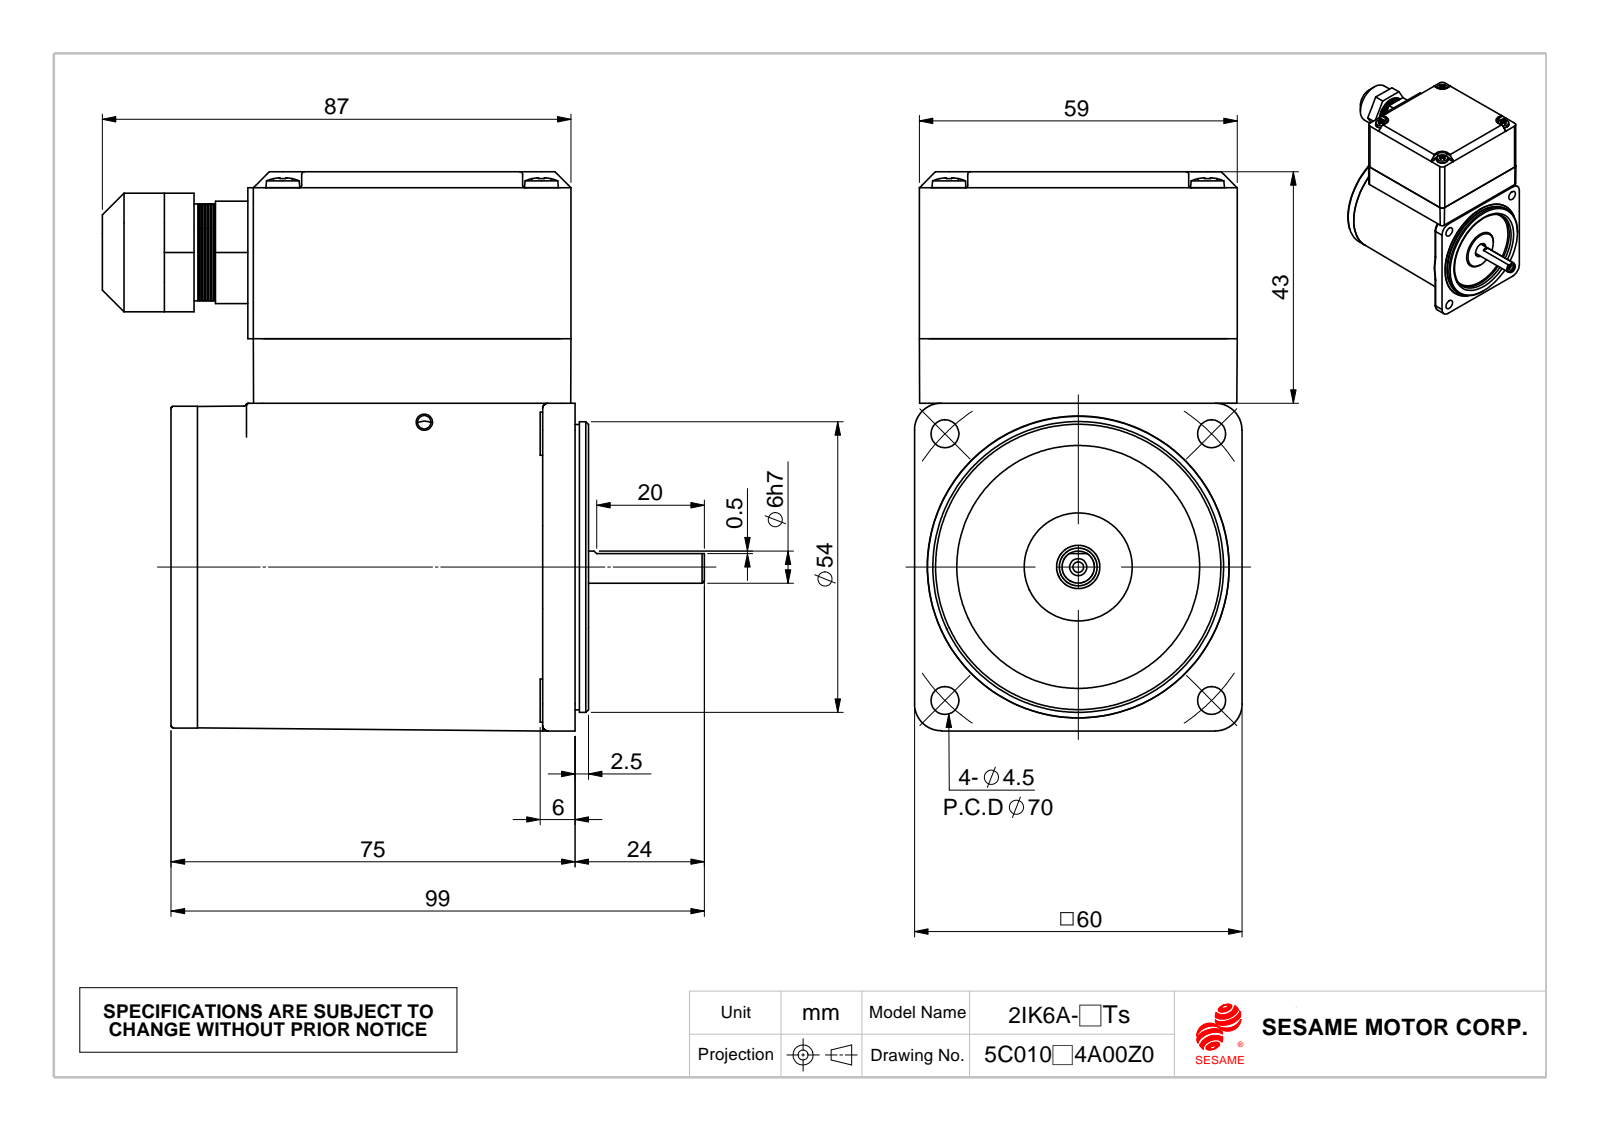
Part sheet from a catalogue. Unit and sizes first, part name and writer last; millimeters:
Units: millimetres
Overall size (bounding box): 111.75 × 103.8 × 60.8
Round holes (diameter × count): ⌀3.3 ×4, ⌀3.5 ×4, ⌀3.9 ×4, ⌀4.3 ×4, ⌀5.2 ×4, ⌀2 ×1, ⌀2.5 ×1, ⌀7 ×1, ⌀11 ×1, ⌀12 ×1, ⌀14.5 ×1, ⌀32.2 ×1
Round bosses / shafts (diameter × count): ⌀8 ×4, ⌀6.3 ×4, ⌀3 ×4, ⌀59.7 ×1, ⌀53.93 ×1, ⌀52.93 ×1, ⌀22 ×1, ⌀18 ×1
Partial cylindrical surfaces — rounded edges, fillets, slot ends (radius × count): R0.5 ×13, R2 ×12, R4 ×6, R1 ×4, R1.5 ×4, R3 ×4, R3.5 ×4, R5 ×4
Main face-to-face distances: 12, 0.75, 31, 43, 1.5, 59, 1, 73.4, 73.5, 75
Hole centre spacings: 35, 48, 49.5, 11.67, 12.35, 12.7, 24.93, 25
Volume: 377 054 mm³ · Surface area: 63 979 mm²
Bodies: 11 solids, 2402 faces (197 planar, 813 cylindrical, 1392 other)
Part name (STEP PRODUCT): C254_Default; 06A_0成品; 成品180度; Ts下墊片 (+1 more)
STEP written by: SolidWorks 2010 (CONFIG_CONTROL_DESIGN)
